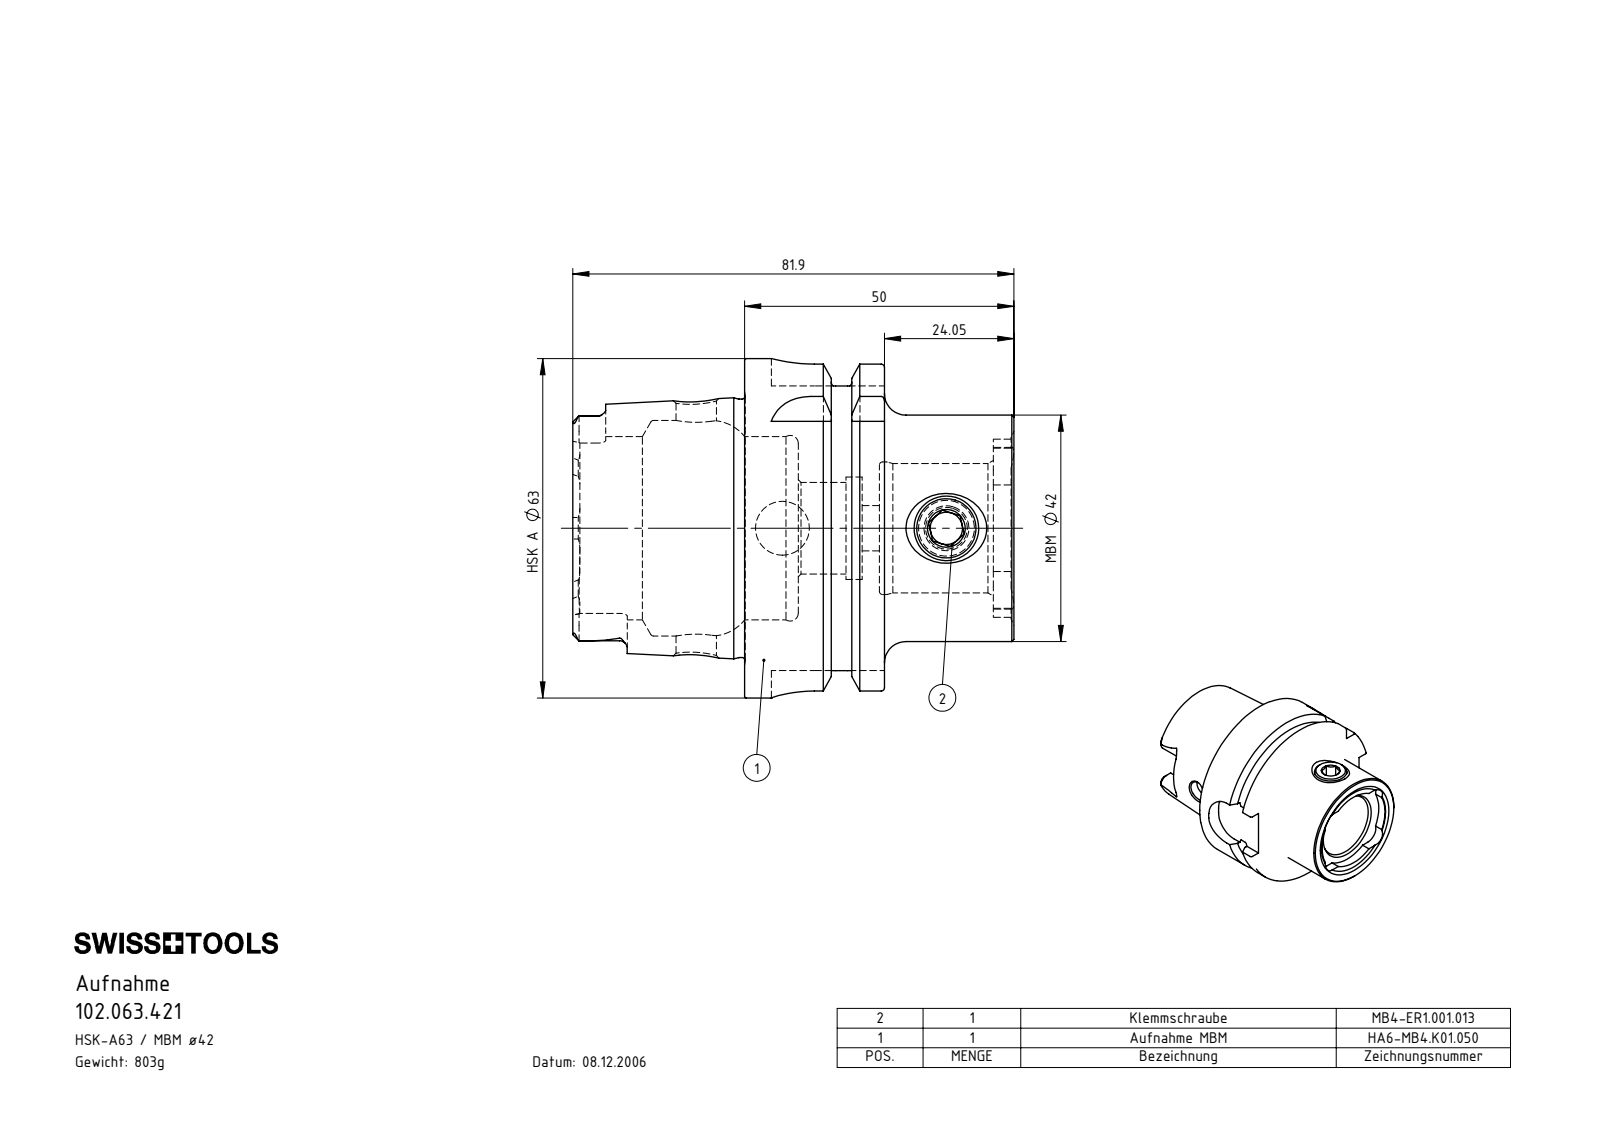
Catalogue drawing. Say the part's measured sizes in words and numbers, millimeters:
The part is named "HA6.MB4.K01.050; MB4-ER1.001.013_A; HA6-MB4.K01.050_A_Fertigbearbeitung". Its 3-D file was written by "SolidWorks 2012 (CONFIG_CONTROL_DESIGN)". It is 2 solids with 226 faces: 64 planar, 64 cylindrical and 98 other. Overall it measures 81.9 by 63 by 63 millimeters. Its volume is 102 259 cubic millimeters and its surface area 27 931 square millimeters. Round holes: 1 of diameter 7.5, 1 of diameter 8.4, 1 of diameter 10, 1 of diameter 11, 1 of diameter 17, 1 of diameter 19, 1 of diameter 24, 1 of diameter 24.6, 1 of diameter 34, 1 of diameter 40. Round bosses or shafts: 1 of diameter 63, 1 of diameter 54.95, 1 of diameter 47.94, 1 of diameter 42, 1 of diameter 12. Partial cylindrical surfaces (rounded edges, fillets, slot ends): 6 of radius 1.4, 4 of radius 2.88, 4 of radius 5.2, 4 of radius 8, 1 of radius 14.9, 1 of radius 16.52. The main face-to-face distances are 25.95, 25, 16, 9.95, 15.05, 0.95, 31.9, 41.85, 56.9, 57.85. The hole center spacings are 30.45.
